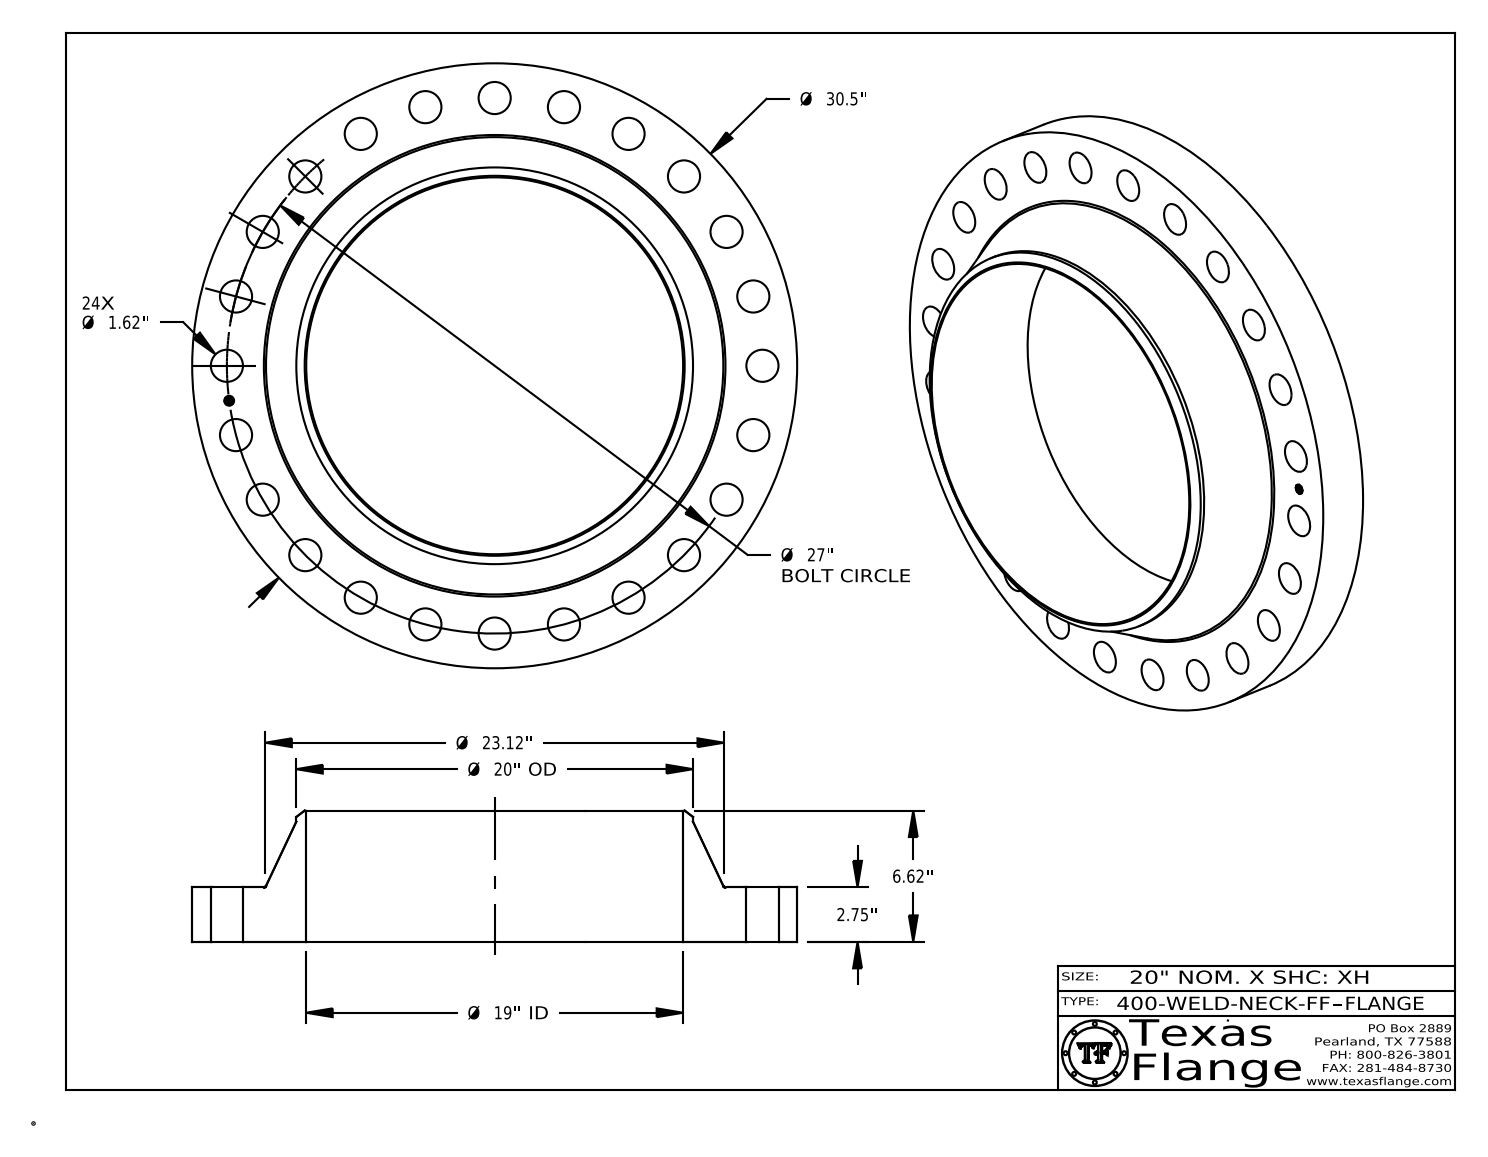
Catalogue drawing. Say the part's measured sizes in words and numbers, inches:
The part is named "400-WELD-NECK-FF". Its 3-D file was written by "CATIA V5 STEP AP214 (AUTOMOTIVE_DESIGN)". It is 1 solid with 448 faces: 368 planar, 74 cylindrical and 6 other. Overall it measures 30.5 by 30.5 by 6.62 inches. Its volume is 1 379 cubic inches and its surface area 1 952 square inches. Round holes: 24 of diameter 1.62, 1 of diameter 0.495, 1 of diameter 19. Round bosses or shafts: 8 of diameter 0.03, 1 of diameter 30.5, 1 of diameter 20, 1 of diameter 0.39. The main face-to-face distances are 2.75, 6.62, 3.87, 2.735, 0.015, 3.885, 0.148, 0.144, 0.027, 0.096. The hole center spacings are 13.5, 3.524, 6.988, 10.333, 16.437, 24.945, 26.769, 21.421.
